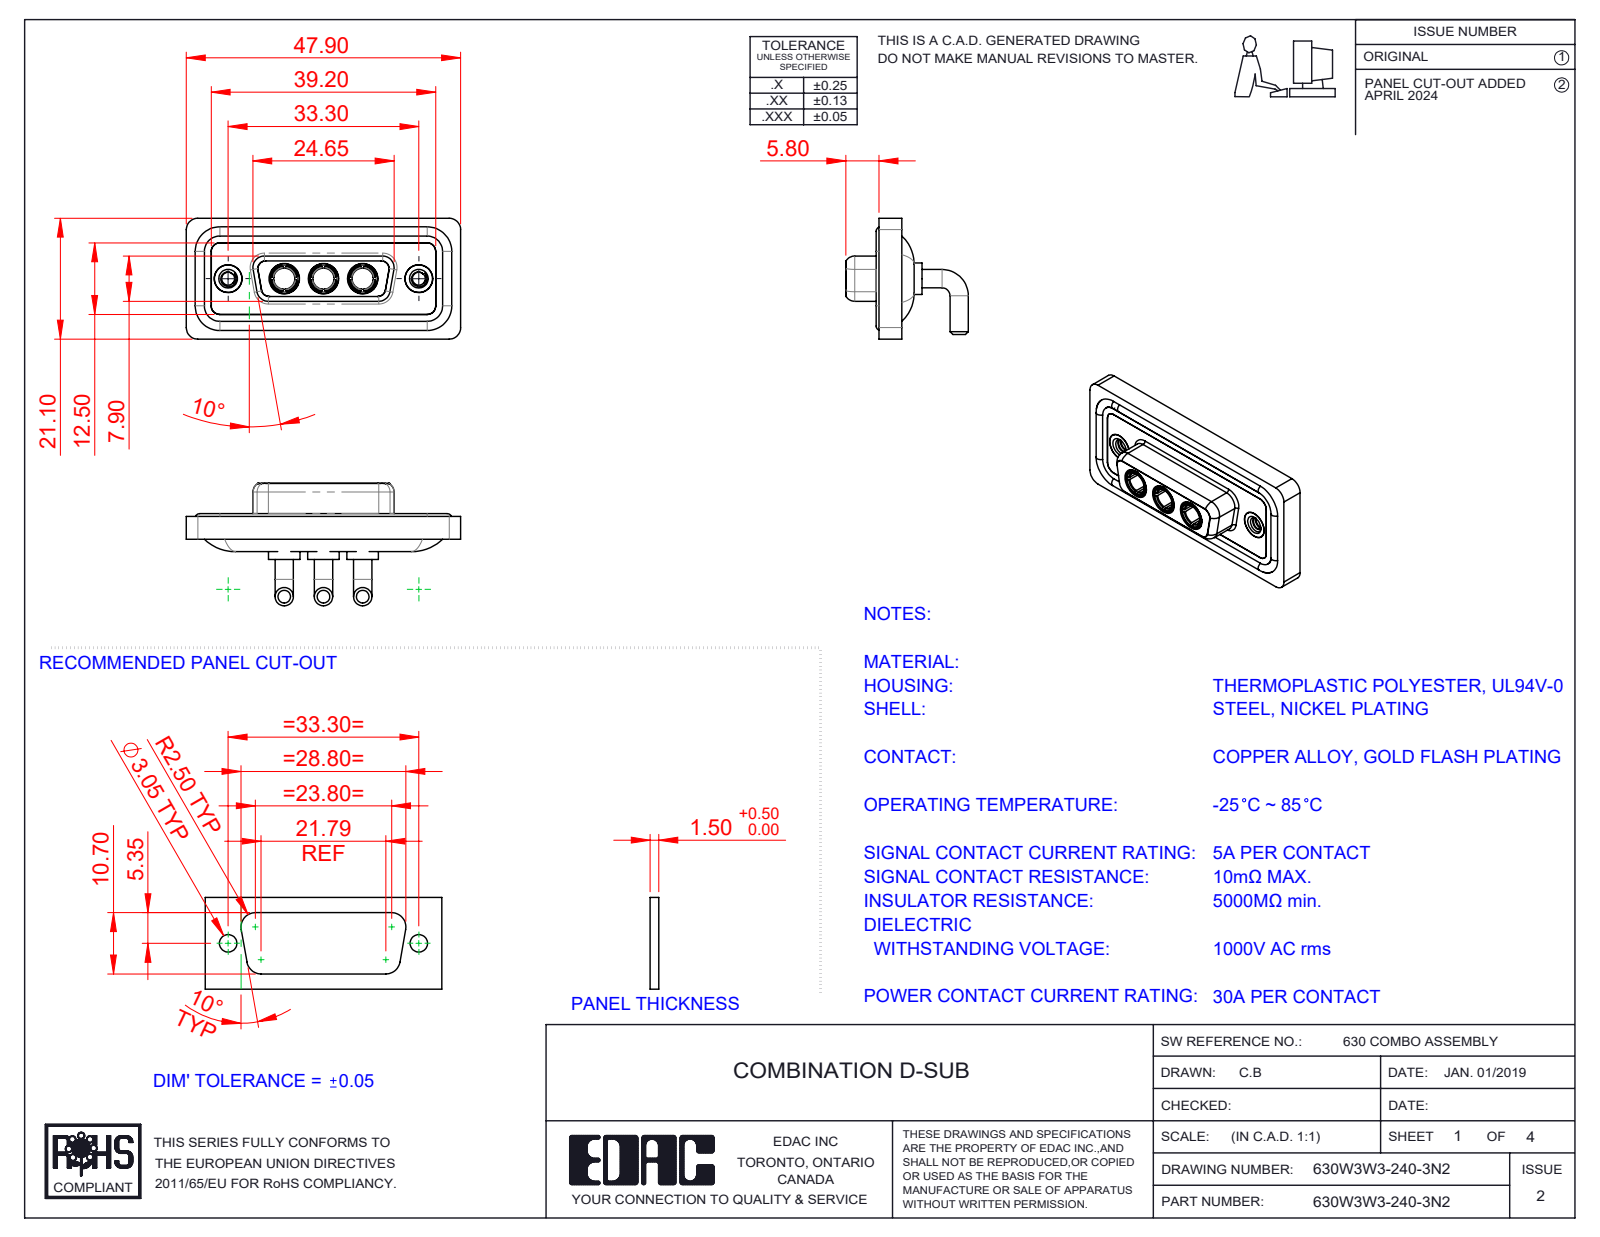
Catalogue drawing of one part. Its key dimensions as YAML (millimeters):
part_name: "630Combo Shell Rear_15 Contacts; 630Combo Waterproof Housing_15 Contacts; Power Socket_30A RA; 630W3W3-140-3N2 (+3 more)"
step_written_by: "SolidWorks 2023 (CONFIG_CONTROL_DESIGN)"
units: millimeters
bodies: {solids: 13, faces: 620, planar: 192, cylindrical: 263, other: 165}
overall_size: [47.9, 21.4, 21.1]
volume: 6264
surface_area: 10027
round_holes:
  - {diameter: 4.85, count: 5}
  - {diameter: 3.7, count: 3}
  - {diameter: 5.3, count: 3}
  - {diameter: 2.26, count: 2}
  - {diameter: 4, count: 2}
  - {diameter: 4.05, count: 2}
  - {diameter: 5, count: 2}
round_bosses_or_shafts:
  - {diameter: 3.2, count: 6}
  - {diameter: 1.6, count: 4}
  - {diameter: 5.5, count: 3}
  - {diameter: 5.2, count: 3}
  - {diameter: 4.96, count: 3}
  - {diameter: 4.75, count: 3}
  - {diameter: 3.75, count: 3}
  - {diameter: 4.95, count: 2}
partial_cylinders:
  - {radius: 2, count: 20}
  - {radius: 1.5, count: 18}
  - {radius: 1.35, count: 12}
  - {radius: 1.6, count: 8}
  - {radius: 0.25, count: 4}
  - {radius: 0.5, count: 4}
  - {radius: 0.6, count: 4}
  - {radius: 0.65, count: 4}
face_to_face_distances: [0.4, 1.8, 1.1, 1.6, 2.9, 2.5, 3.1, 3.7, 4.1, 1.5]
hole_center_spacings: [6.85, 9.8, 16.65, 23.5, 13.7, 33.3]
